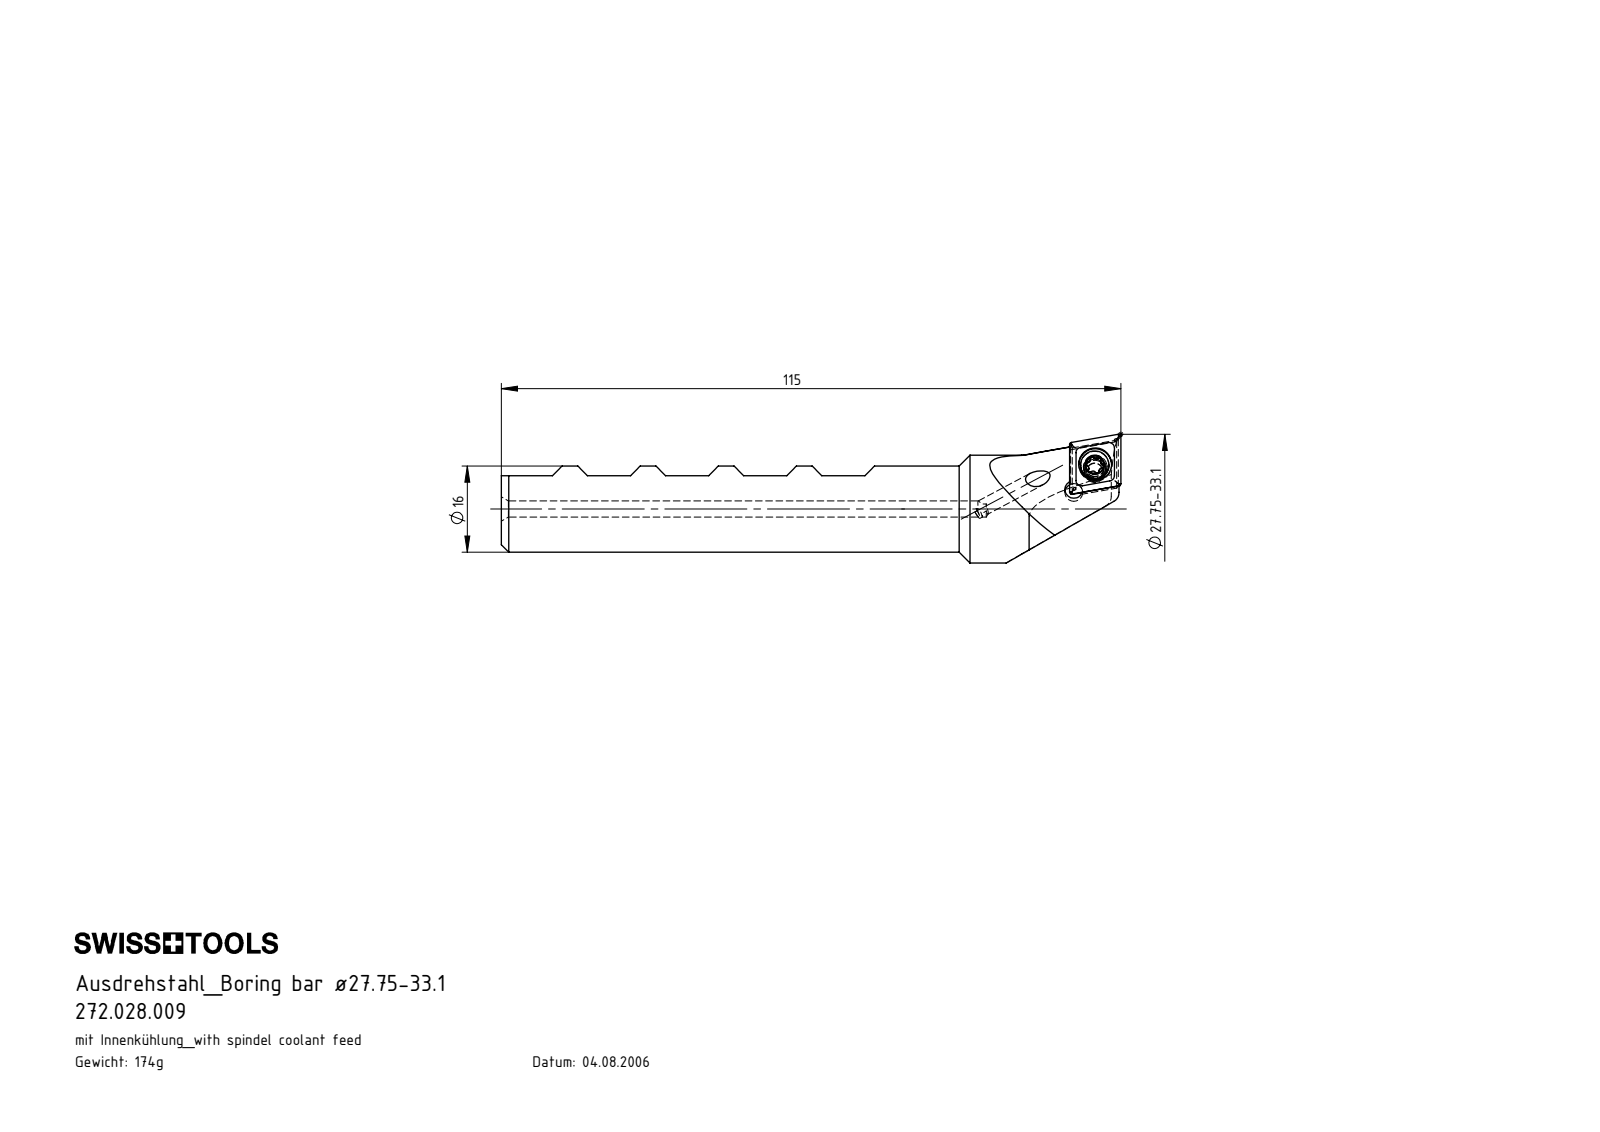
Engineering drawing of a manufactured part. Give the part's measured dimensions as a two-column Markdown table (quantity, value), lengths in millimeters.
| quantity | value |
| --- | --- |
| part name | CCMT09T304; WCB-ER2.001.009_A; B28-WCB.K11.115_A; B28-WCB.K11.115 |
| STEP written by | SolidWorks 2012 (CONFIG_CONTROL_DESIGN) |
| units | millimeters |
| bodies | 3 solids, 147 faces (45 planar, 41 cylindrical, 61 other) |
| overall size | 115 × 23.88 × 21.36 |
| volume | 22 165 mm³ |
| surface area | 7 787 mm² |
| round holes (diameter × count) | 3 × 2, 3.3 × 2, 4.4 × 1, 6.1 × 1 |
| round bosses / shafts (diameter × count) | 20 × 1, 16 × 1, 5.25 × 1, 4 × 1 |
| partial cylindrical surfaces (radius × count) | 0.34 × 6, 0.59 × 6, 2 × 1, 10.2 × 1, 12 × 1 |
| main face-to-face distances | 10.25, 8.16, 20.5, 20.51, 30.76, 11.93, 3.77, 12.13, 3.97, 10.26 |
| hole center spacings | 6.07, 6.19 |
